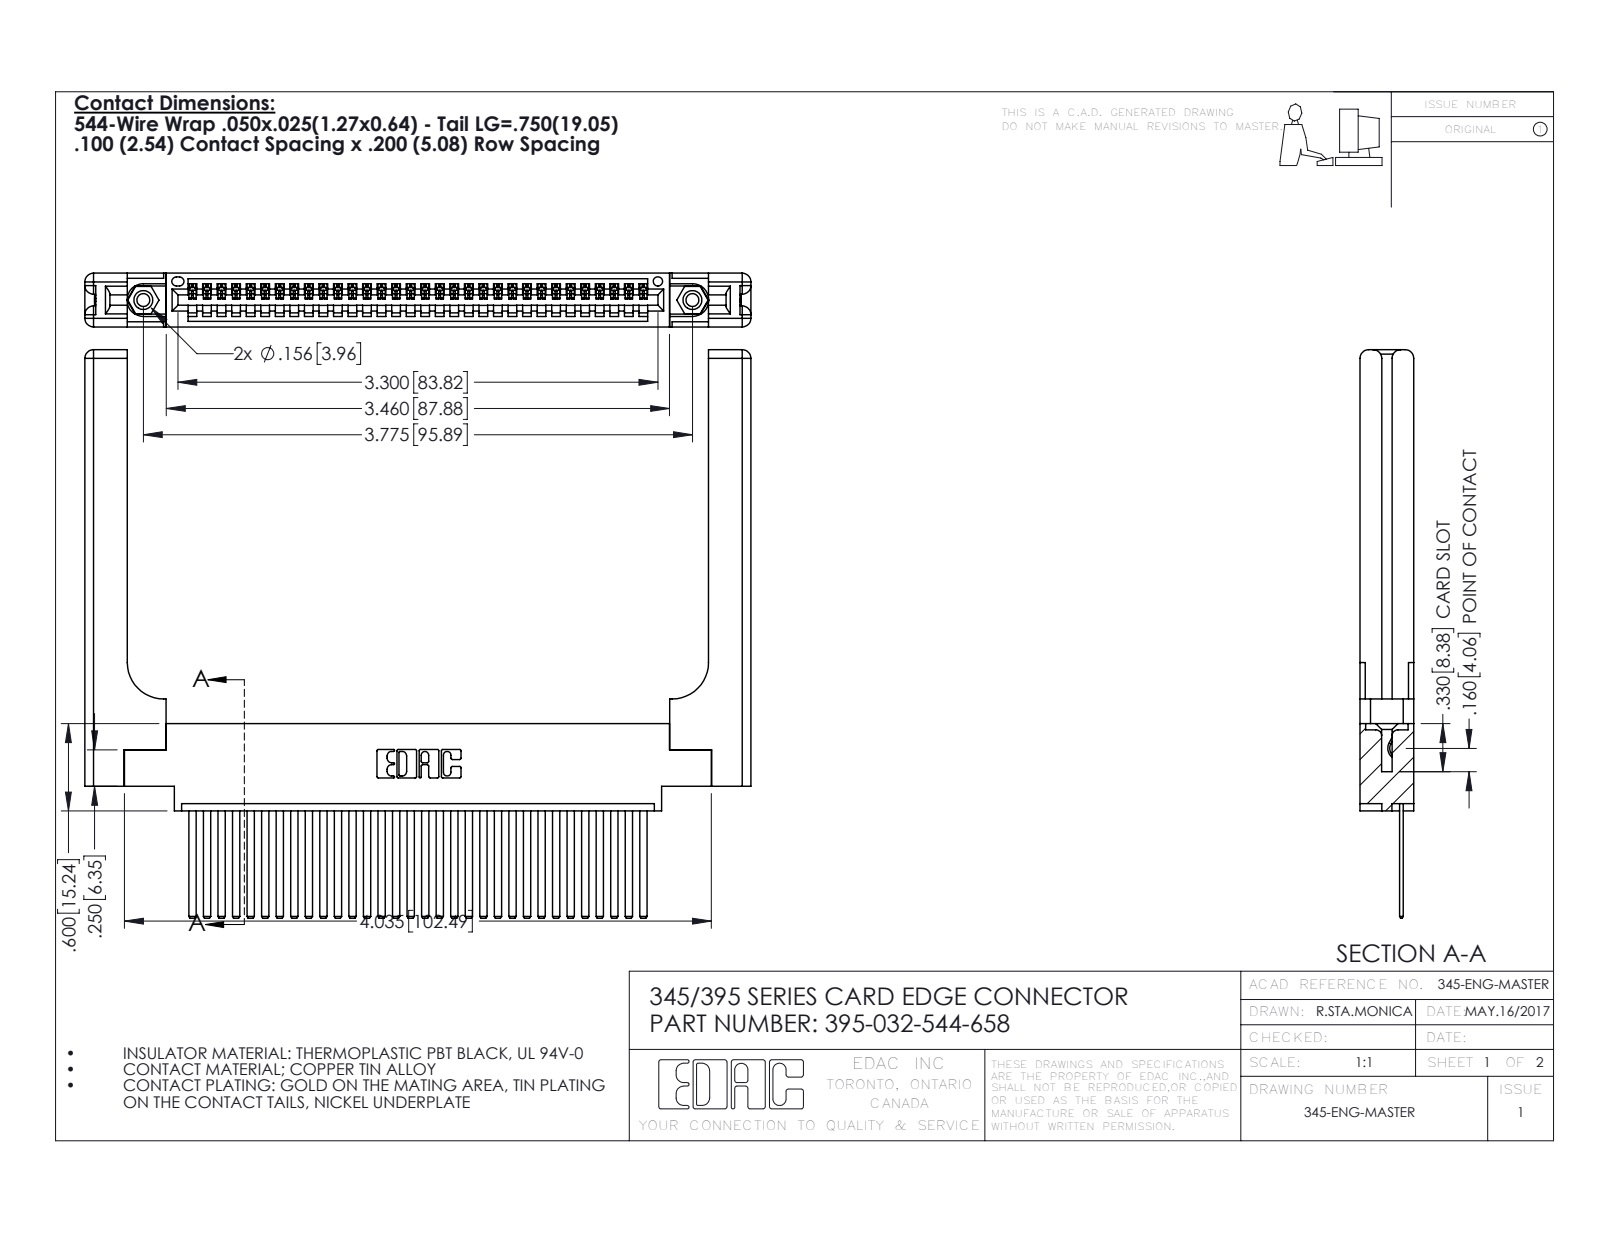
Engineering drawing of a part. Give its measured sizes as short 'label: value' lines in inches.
name: 345-250-001_345-250-001-102; 345-292-001_345-293-144; 345 Part_0.170 Offset - 0.156 Dia-TH; 395-032-544-658 (+1 more)
written by: SolidWorks 2016 (CONFIG_CONTROL_DESIGN)
unit: in
bodies: 37 solids, 2050 faces (1384 planar, 606 cylindrical, 60 other)
size: 4.579 × 3.907 × 0.37
volume: 1.204 in³; area: 33.05 in²
holes: 2× ⌀0.089, 2× ⌀0.125, 2× ⌀0.156, 1× ⌀0.064
bosses: 2× ⌀0.155
rounds: 64× R0.006, 22× R0.01, 16× R0.06, 6× R0.007, 6× R0.031, 3× R0.026, 2× R0.03, 2× R0.031
face distances: 0.072, 0.37, 0.298, 0.098, 0.272, 0.025, 0.2, 0.148, 0.15, 0.077
hole spacings: 0.27, 3.54, 3.775
